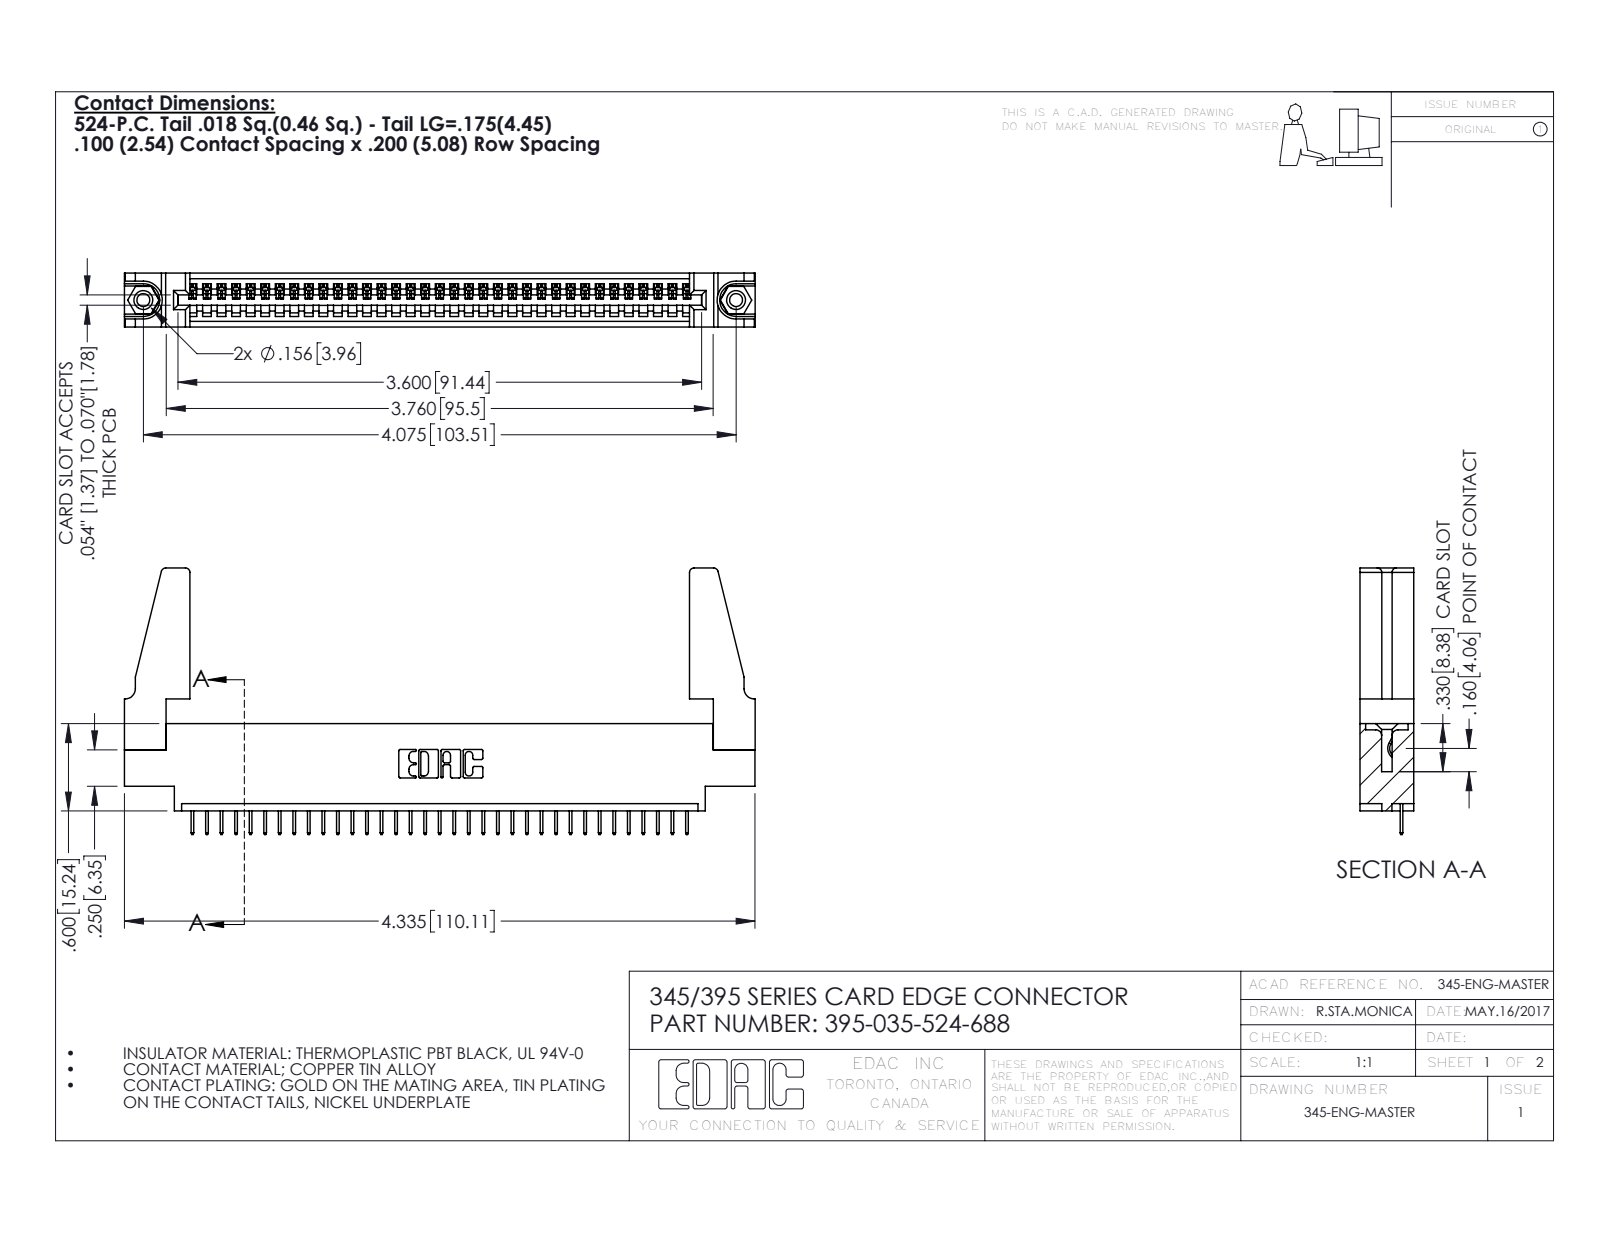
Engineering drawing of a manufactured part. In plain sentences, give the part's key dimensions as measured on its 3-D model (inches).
The part is named "395-035-524-688; 345-250-001_345-250-001-102; 345-292-001_345-293-124; 345 Part_0.170 Offset - 0.156 Dia-TH (+1 more)". Its 3-D file was written by "SolidWorks 2016 (CONFIG_CONTROL_DESIGN)". It is 40 solids with 2424 faces: 1766 planar, 642 cylindrical and 16 other. Overall it measures 4.336 by 1.832 by 0.37 inches. Its volume is 0.818 cubic inches and its surface area 25.12 square inches. Round holes: 2 of diameter 0.089, 2 of diameter 0.125, 2 of diameter 0.156, 1 of diameter 0.064. Round bosses or shafts: 2 of diameter 0.155. Partial cylindrical surfaces (rounded edges, fillets, slot ends): 70 of radius 0.006, 22 of radius 0.01, 8 of radius 0.03, 6 of radius 0.007, 6 of radius 0.031, 3 of radius 0.026, 2 of radius 0.031, 2 of radius 0.04. The main face-to-face distances are 0.37, 0.072, 0.298, 0.098, 0.272, 0.025, 0.2, 0.225, 0.072, 0.175. The hole center spacings are 0.27, 3.839, 4.075.
